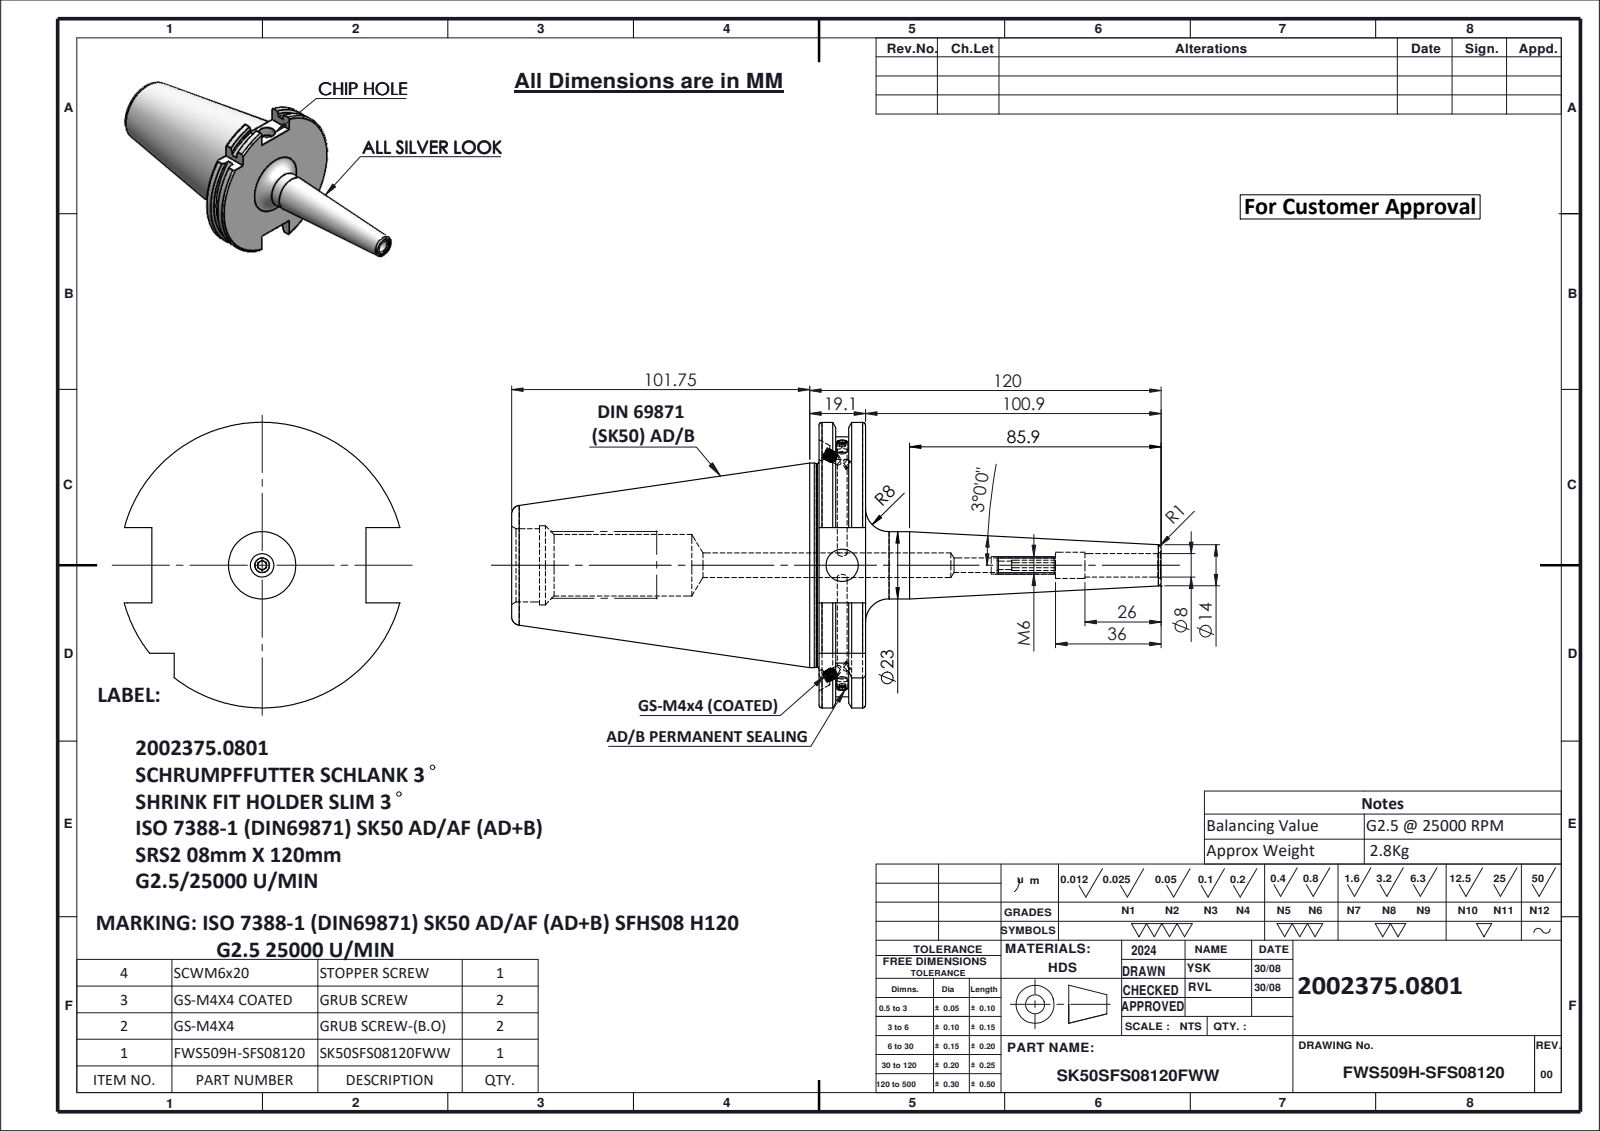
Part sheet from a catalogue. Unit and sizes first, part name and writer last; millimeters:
Units: millimetres
Overall size (bounding box): 221.75 × 97.5 × 94.05
Round holes (diameter × count): ⌀3.2 ×2, ⌀6 ×2, ⌀2.9 ×1, ⌀3.3 ×1, ⌀5 ×1, ⌀8 ×1, ⌀8.4 ×1, ⌀9 ×1, ⌀11 ×1, ⌀21 ×1, ⌀25 ×1, ⌀27 ×1
Round bosses / shafts (diameter × count): ⌀4 ×4, ⌀2.9 ×2, ⌀69.85 ×1, ⌀69.45 ×1, ⌀23 ×1, ⌀6 ×1
Partial cylindrical surfaces — rounded edges, fillets, slot ends (radius × count): R44.9 ×1, R48.75 ×1
Main face-to-face distances: 15.9, 5.65, 10.25, 10.14, 4.49, 5.76, 104.95, 110.6, 115.09, 120.85
Volume: 361 820 mm³ · Surface area: 51 966 mm²
Bodies: 6 solids, 275 faces (72 planar, 81 cylindrical, 122 other)
Part name (STEP PRODUCT): SCWM6; SK50SFS08120FWW; GS-M4X4-COATING_DIN 913 - M4 x 4-N; GS-M4X4_DIN 913 - M4 x 4-N (+1 more)
STEP written by: SolidWorks 2024 (CONFIG_CONTROL_DESIGN)
